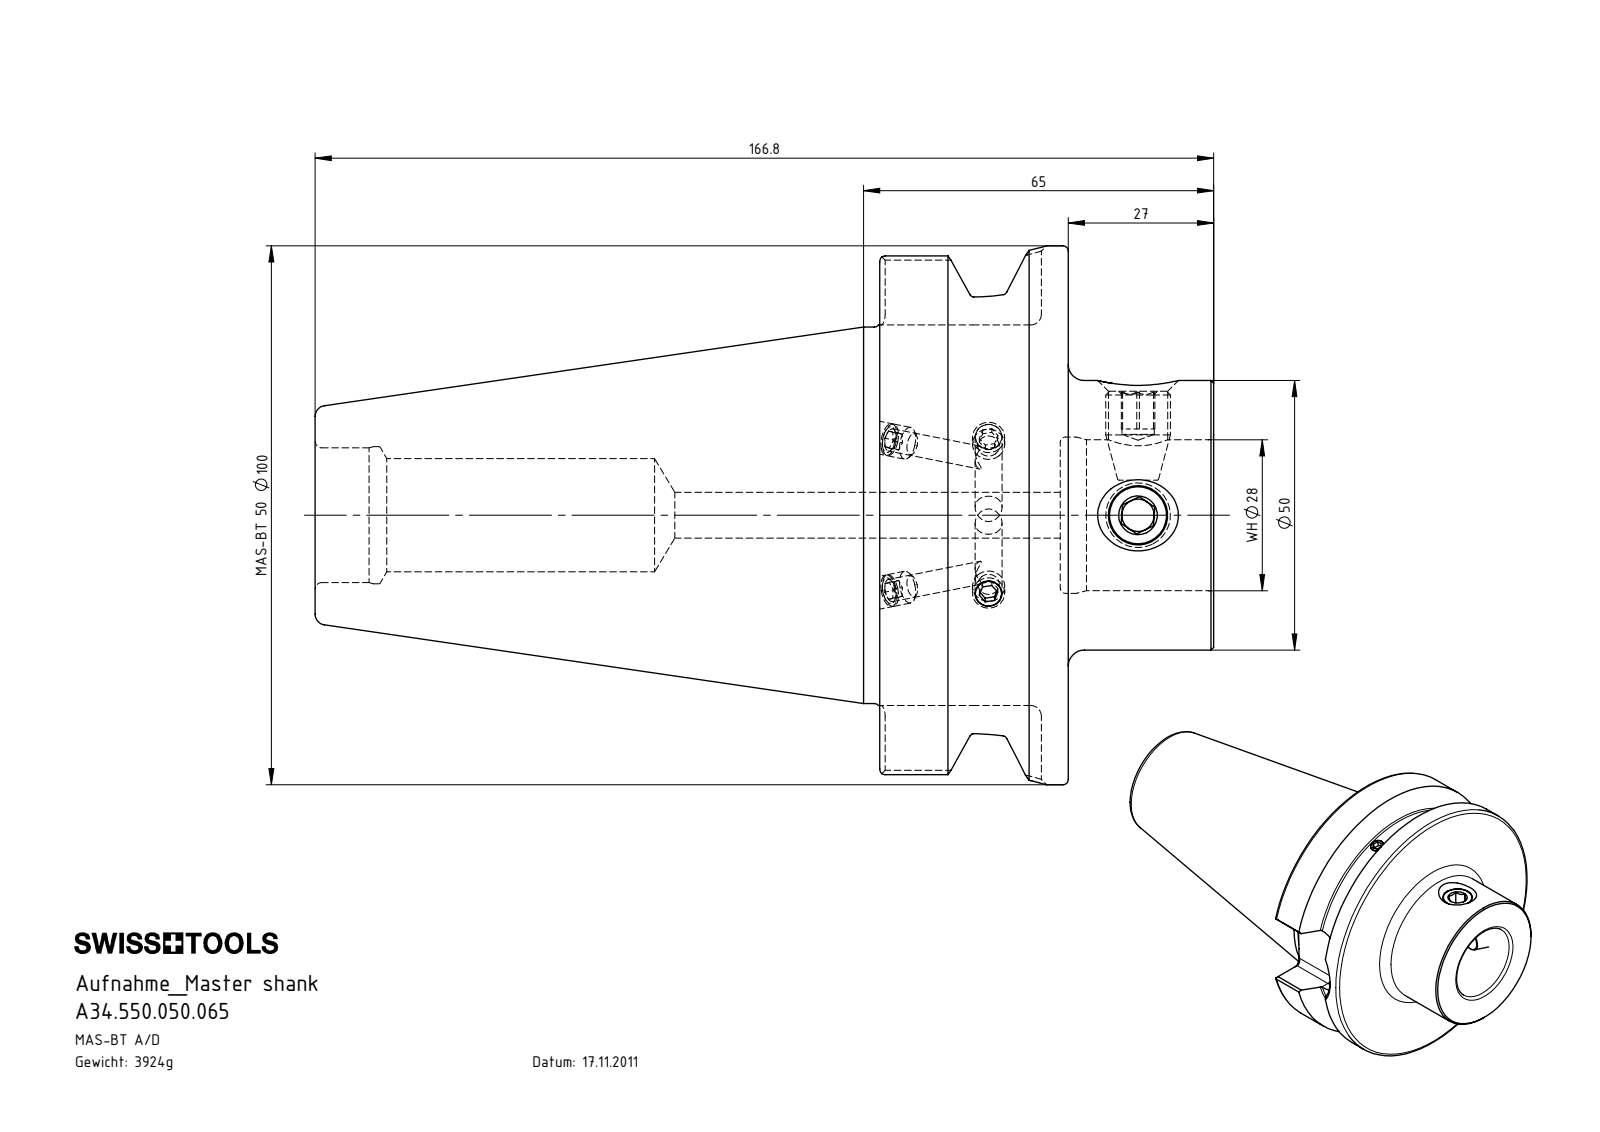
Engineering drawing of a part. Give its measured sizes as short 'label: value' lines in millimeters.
name: BB5-WH5.K01.065_B; ISO 4026 - M6 x 5_PreviewCfg; BB5-WH5.K01.065; WH5-ER1.001.017
written by: SolidWorks 2015 (AUTOMOTIVE_DESIGN)
unit: mm
bodies: 7 solids, 240 faces (84 planar, 65 cylindrical, 91 other)
size: 166.8 × 100 × 100
volume: 500 367 mm³; area: 61 342 mm²
holes: 4× ⌀6, 2× ⌀4.2, 2× ⌀11, 1× ⌀5, 1× ⌀8.5, 1× ⌀21, 1× ⌀25, 1× ⌀25.45, 1× ⌀28, 1× ⌀29
bosses: 2× ⌀12, 2× ⌀6, 1× ⌀100, 1× ⌀85, 1× ⌀69.85, 1× ⌀50
rounds: 8× R2, 1× R12.85
face distances: 35, 62, 27, 70.6, 33.5, 1.5, 28.5, 104.8, 138.3, 139.8
